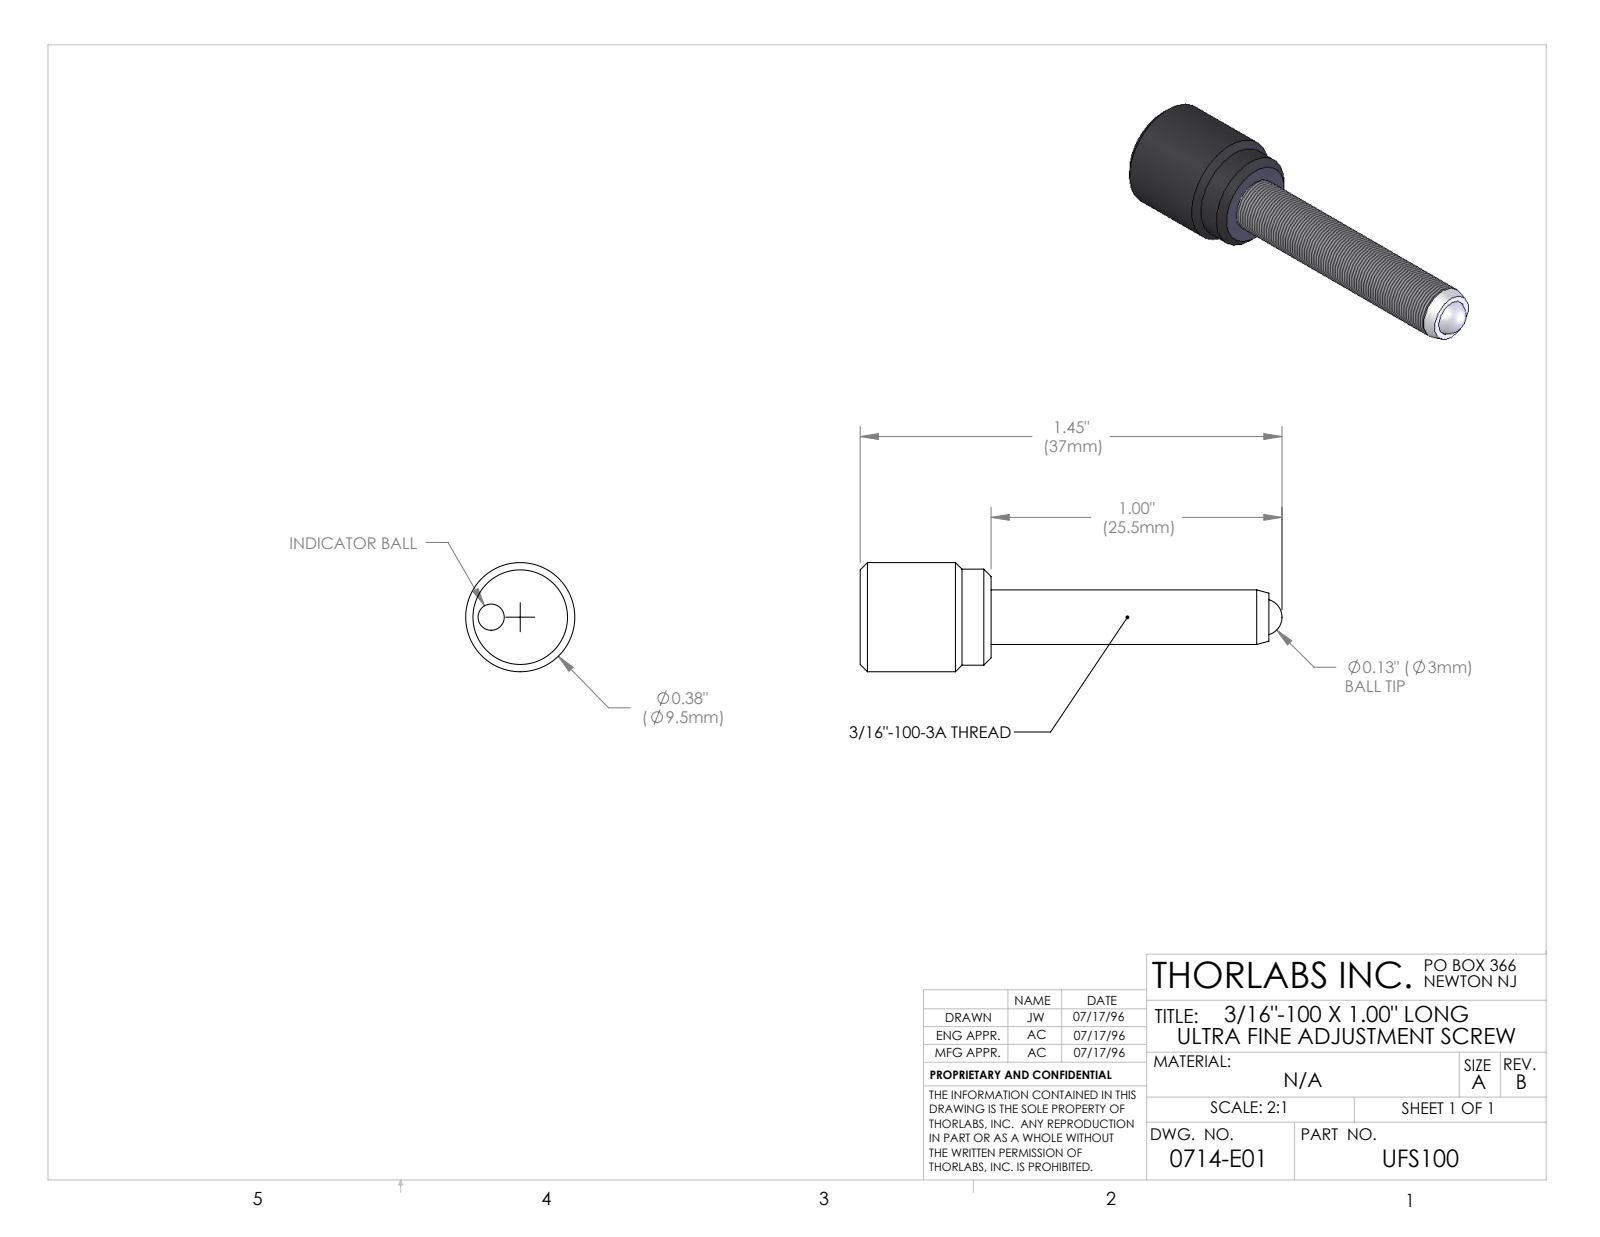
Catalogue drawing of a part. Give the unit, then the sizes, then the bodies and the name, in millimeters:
Units: millimetres
Overall size (bounding box): 36.83 × 9.53 × 9.53
Round holes (diameter × count): ⌀2.29 ×1, ⌀3.19 ×1, ⌀4.57 ×1, ⌀4.72 ×1
Round bosses / shafts (diameter × count): ⌀9.52 ×1, ⌀8.38 ×1, ⌀4.76 ×1
Main face-to-face distances: 3.55, 11.43, 7.88, 35.68, 32.13, 24.25, 2.28, 1.27, 9.15, 33.4
Hole centre spacings: 2.54
Volume: 1 197 mm³ · Surface area: 1 147 mm²
Bodies: 4 solids, 39 faces (7 planar, 14 cylindrical, 18 other)
Part name (STEP PRODUCT): 0714-E0W
STEP written by: SolidWorks 2007 (AUTOMOTIVE_DESIGN)
